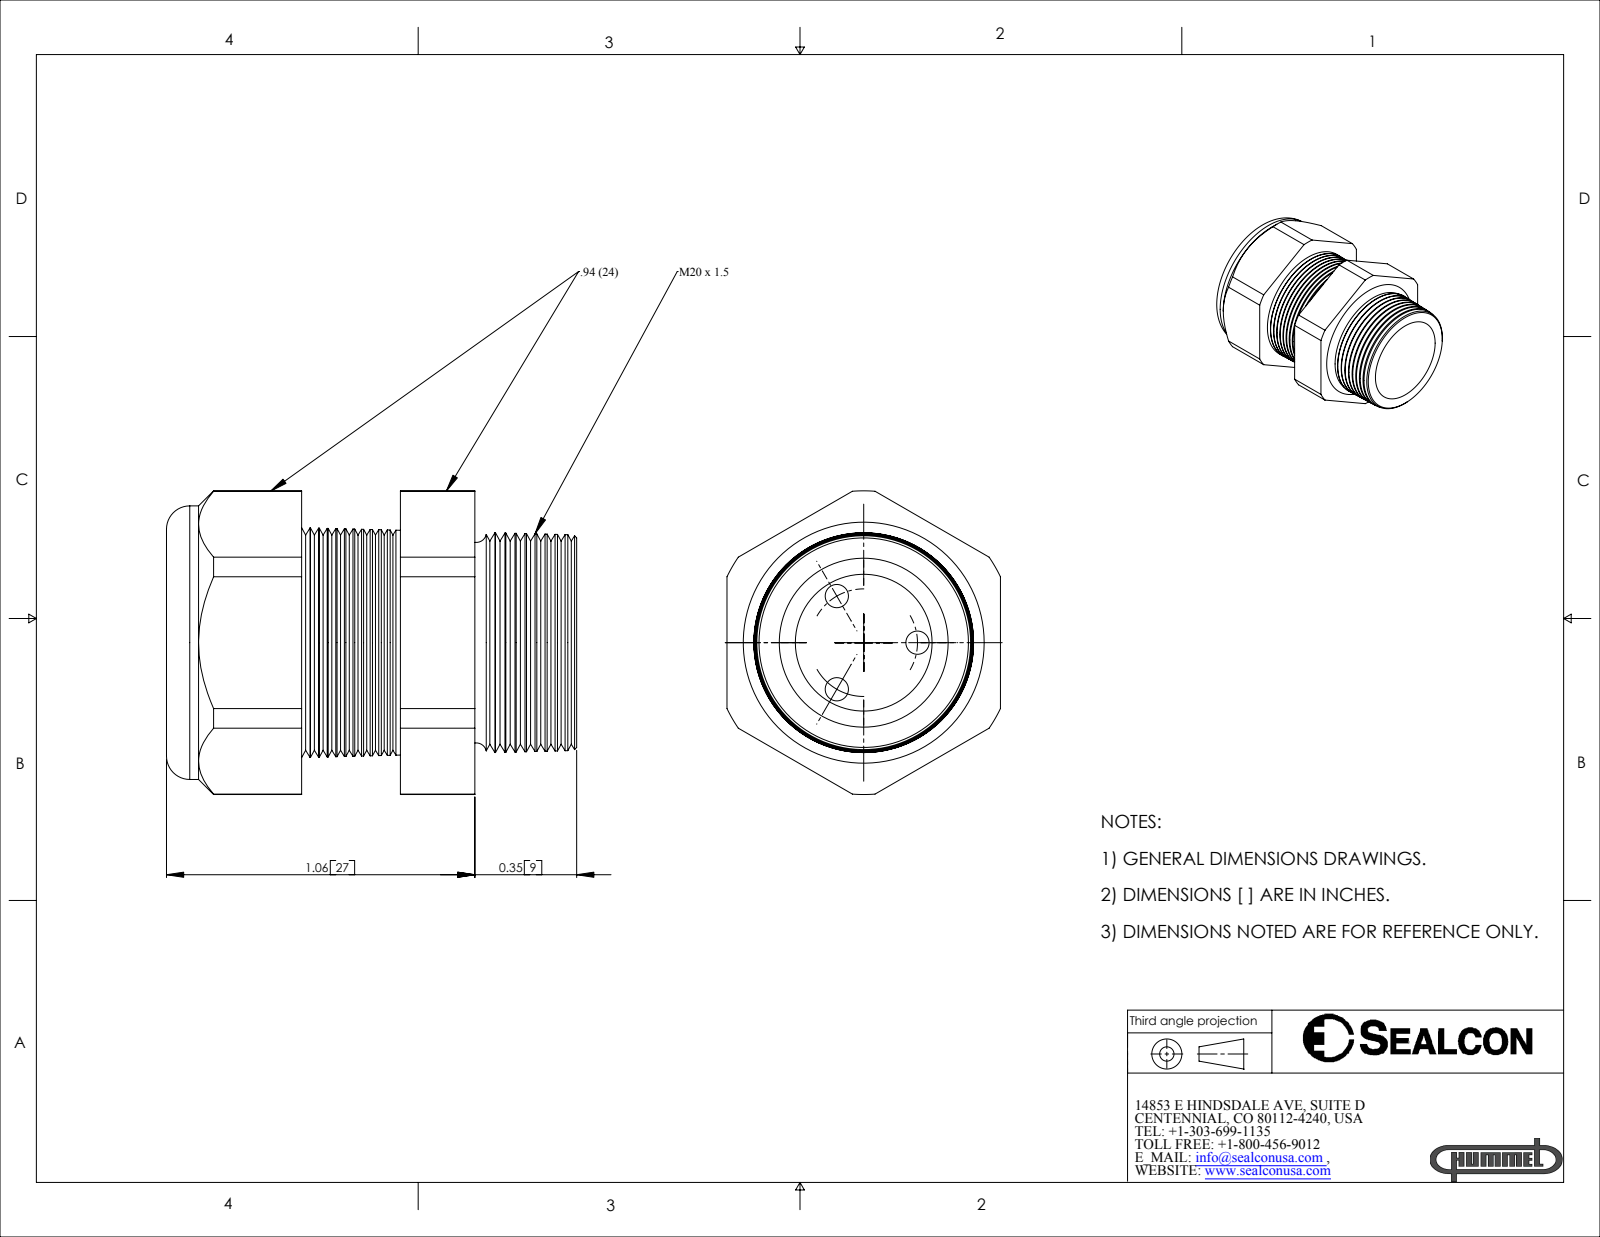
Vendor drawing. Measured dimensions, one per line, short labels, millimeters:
name: CD20M1-BK
written by: SolidWorks 2007 (CONFIG_CONTROL_DESIGN)
unit: mm
bodies: 2 solids, 180 faces (20 planar, 26 cylindrical, 134 other)
size: 35.8 × 26.5 × 23.9
volume: 9 540 mm³; area: 6 377 mm²
holes: 3× ⌀2, 1× ⌀11.4, 1× ⌀11.9
bosses: 1× ⌀23.9
rounds: 1× R13.3
face distances: 23.9, 20.4, 11.8, 8.6, 26.9, 15.1, 6.5, 6.4, 5.5, 14.1
hole spacings: 4.7, 8.1, 4.7, 8.1
